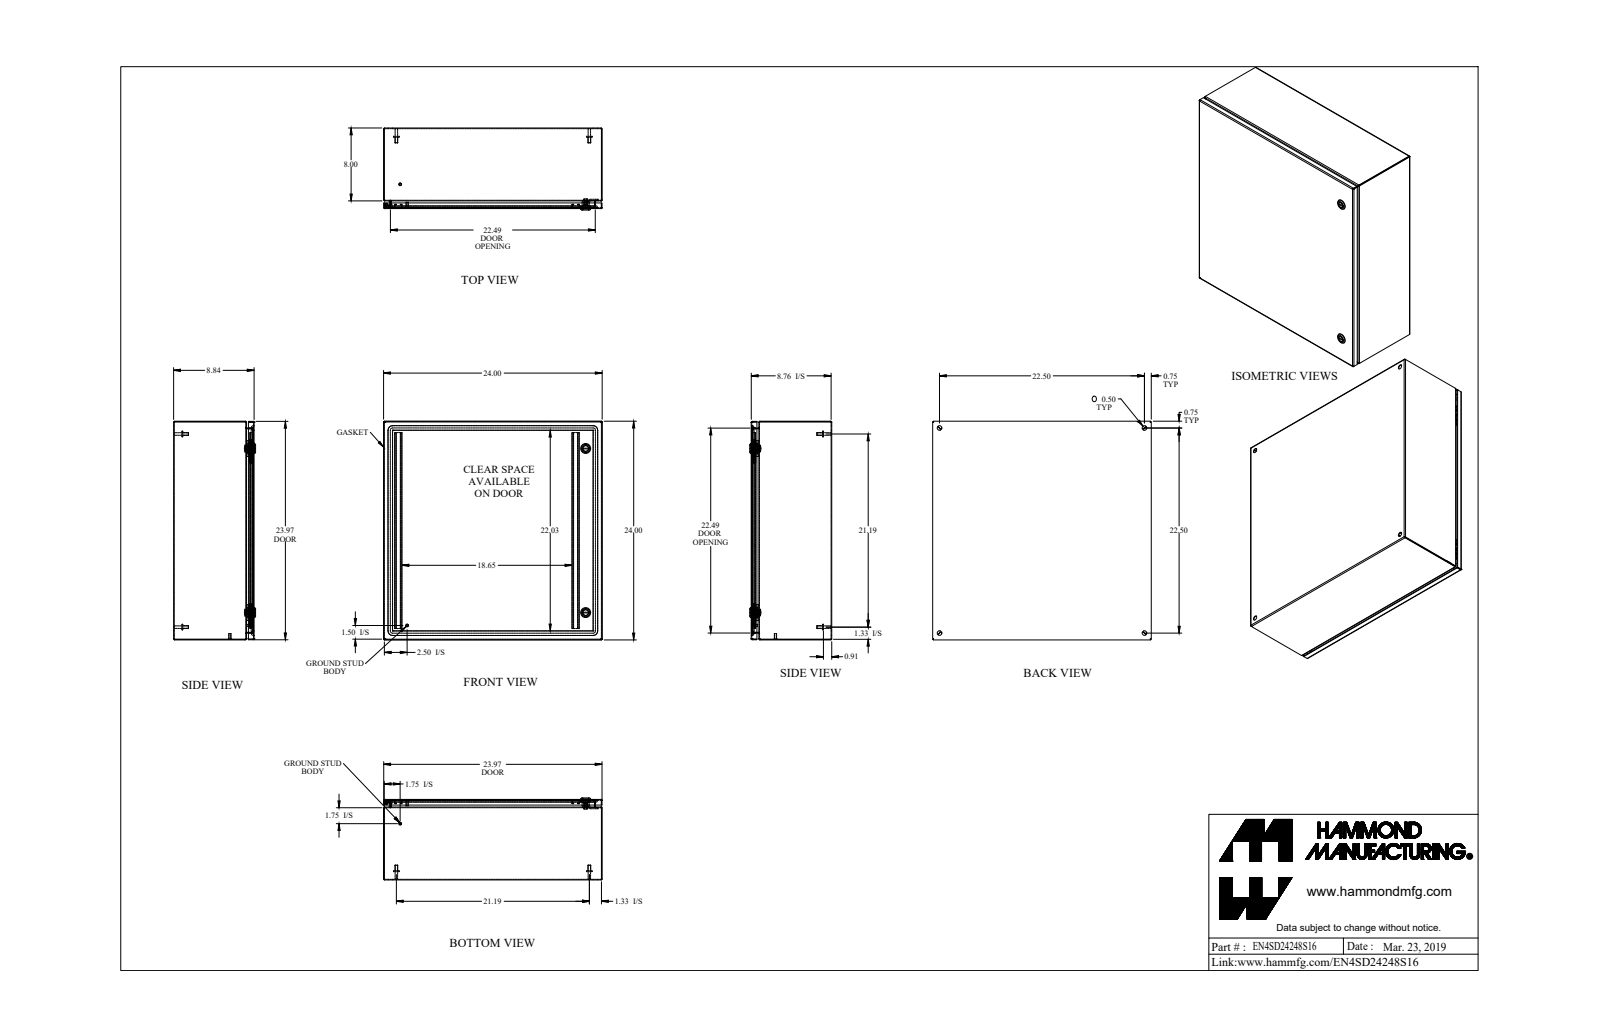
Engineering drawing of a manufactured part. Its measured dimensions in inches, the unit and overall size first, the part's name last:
Units: inches
Overall size (bounding box): 24 × 24 × 9.002
Round holes (diameter × count): ⌀0.5 ×6, ⌀0.197 ×2, ⌀0.387 ×2, ⌀0.63 ×2, ⌀0.768 ×2, ⌀0.172 ×1, ⌀0.24 ×1, ⌀0.242 ×1
Round bosses / shafts (diameter × count): ⌀0.625 ×6, ⌀0.313 ×6, ⌀0.275 ×4, ⌀1.1 ×2, ⌀0.785 ×2, ⌀0.525 ×2, ⌀0.25 ×2, ⌀0.236 ×2
Partial cylindrical surfaces — rounded edges, fillets, slot ends (radius × count): R0.036 ×20, R0.108 ×20, R0.25 ×16, R0.01 ×12, R0.048 ×12, R0.006 ×4, R0.062 ×4, R0.125 ×4
Main face-to-face distances: 0.072, 8.77, 23.928, 8.698, 8.842, 23.856, 24, 0.842, 7.928, 0.75
Hole centre spacings: 22.5, 2.488, 20.278, 21.557, 29.491, 31.82, 18
Volume: 164 in³ · Surface area: 4 597 in²
Bodies: 29 solids, 820 faces (414 planar, 262 cylindrical, 144 other)
Part name (STEP PRODUCT): EN4SD24248S16_Default
STEP written by: SolidWorks 2019 (CONFIG_CONTROL_DESIGN)
